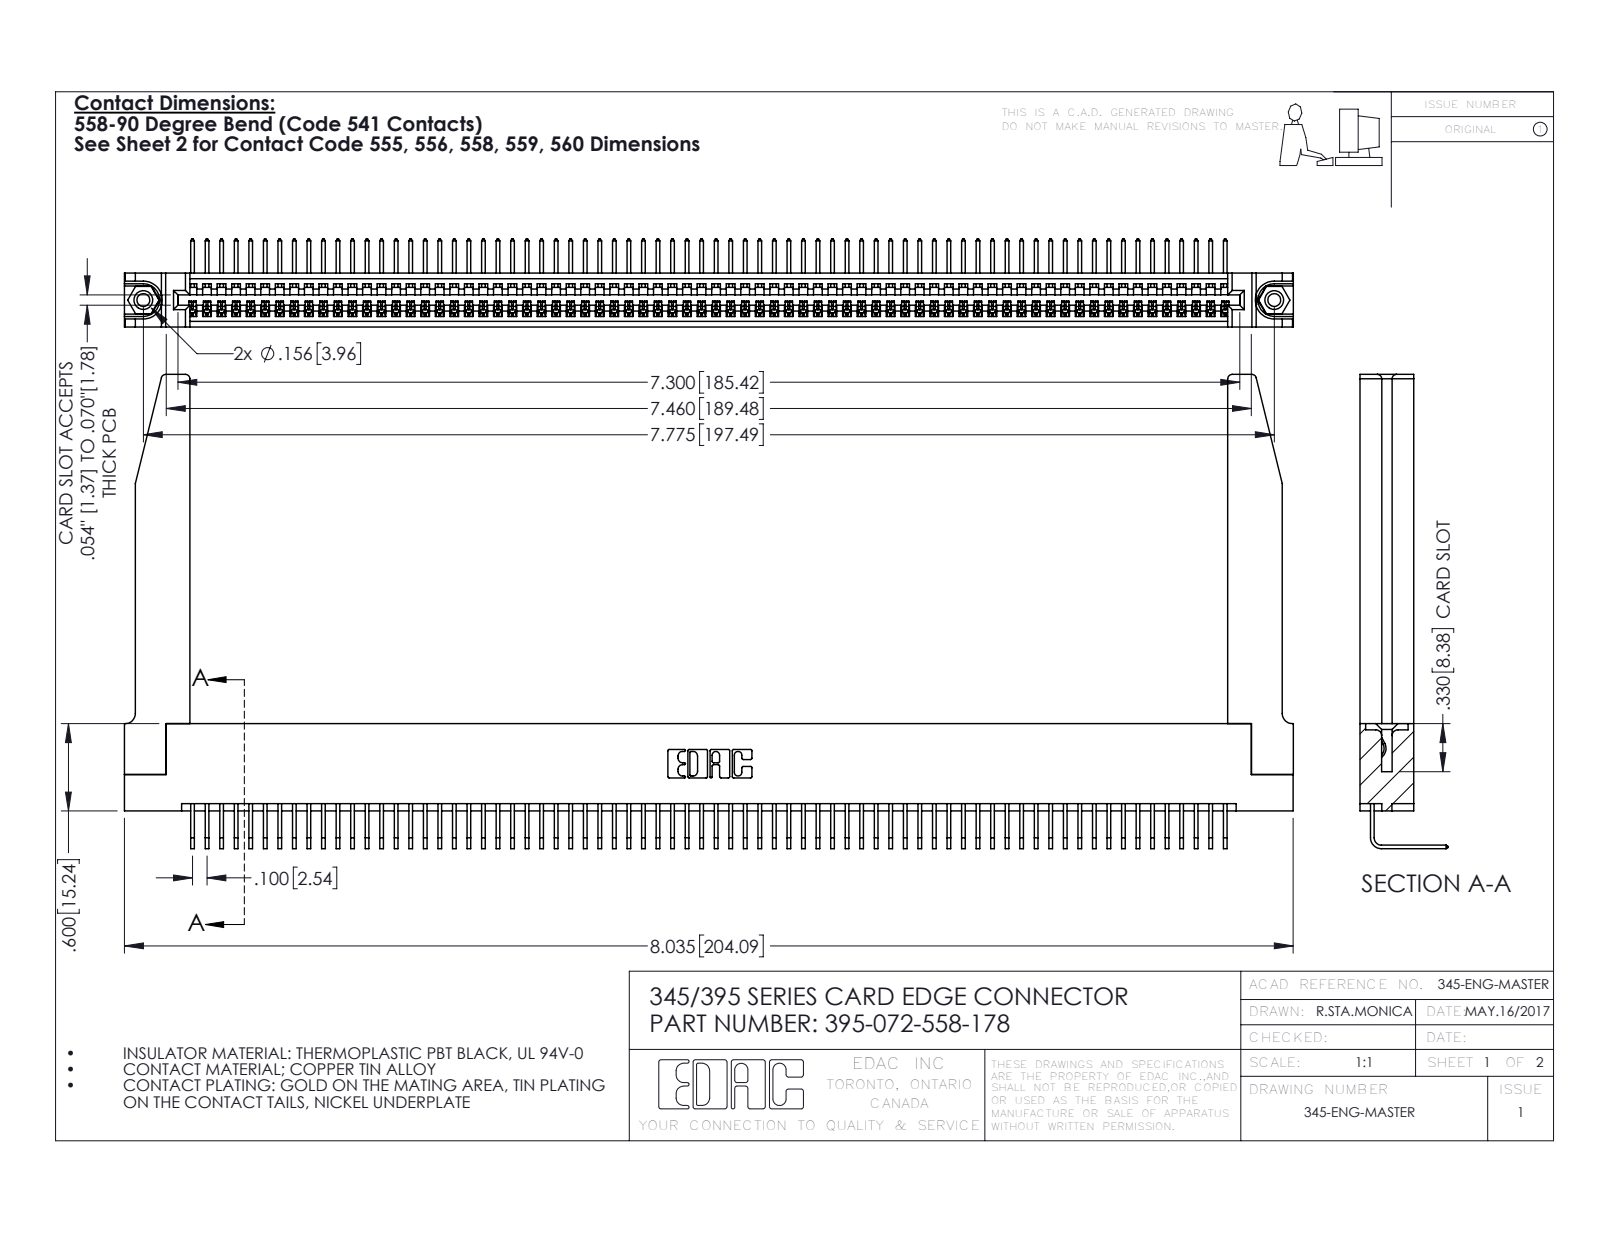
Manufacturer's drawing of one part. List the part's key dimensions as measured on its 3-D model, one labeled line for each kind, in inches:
Part name (STEP PRODUCT): 345 Part_Flush Mounting Lugs - 0.156 Dia-TH; 345-292-001_558 Tail - 2; 395-072-558-178; 345-250-001_345-250-001-102 (+1 more)
STEP written by: SolidWorks 2016 (CONFIG_CONTROL_DESIGN)
Units: inches
Bodies: 77 solids, 4680 faces (3246 planar, 1382 cylindrical, 52 other)
Overall size (bounding box): 8.036 × 3.259 × 0.605
Volume: 1.687 in³ · Surface area: 54.36 in²
Round holes (diameter × count): ⌀0.089 ×2, ⌀0.125 ×2, ⌀0.156 ×2, ⌀0.064 ×1
Round bosses / shafts (diameter × count): ⌀0.155 ×2
Partial cylindrical surfaces — rounded edges, fillets, slot ends (radius × count): R0.006 ×144, R0.01 ×22, R0.03 ×8, R0.007 ×6, R0.031 ×6, R0.026 ×3, R0.031 ×2, R0.04 ×2
Main face-to-face distances: 0.072, 0.37, 0.298, 0.2, 0.098, 0.272, 0.025, 0.225, 0.149, 0.15
Hole centre spacings: 0.27, 7.539, 7.775
